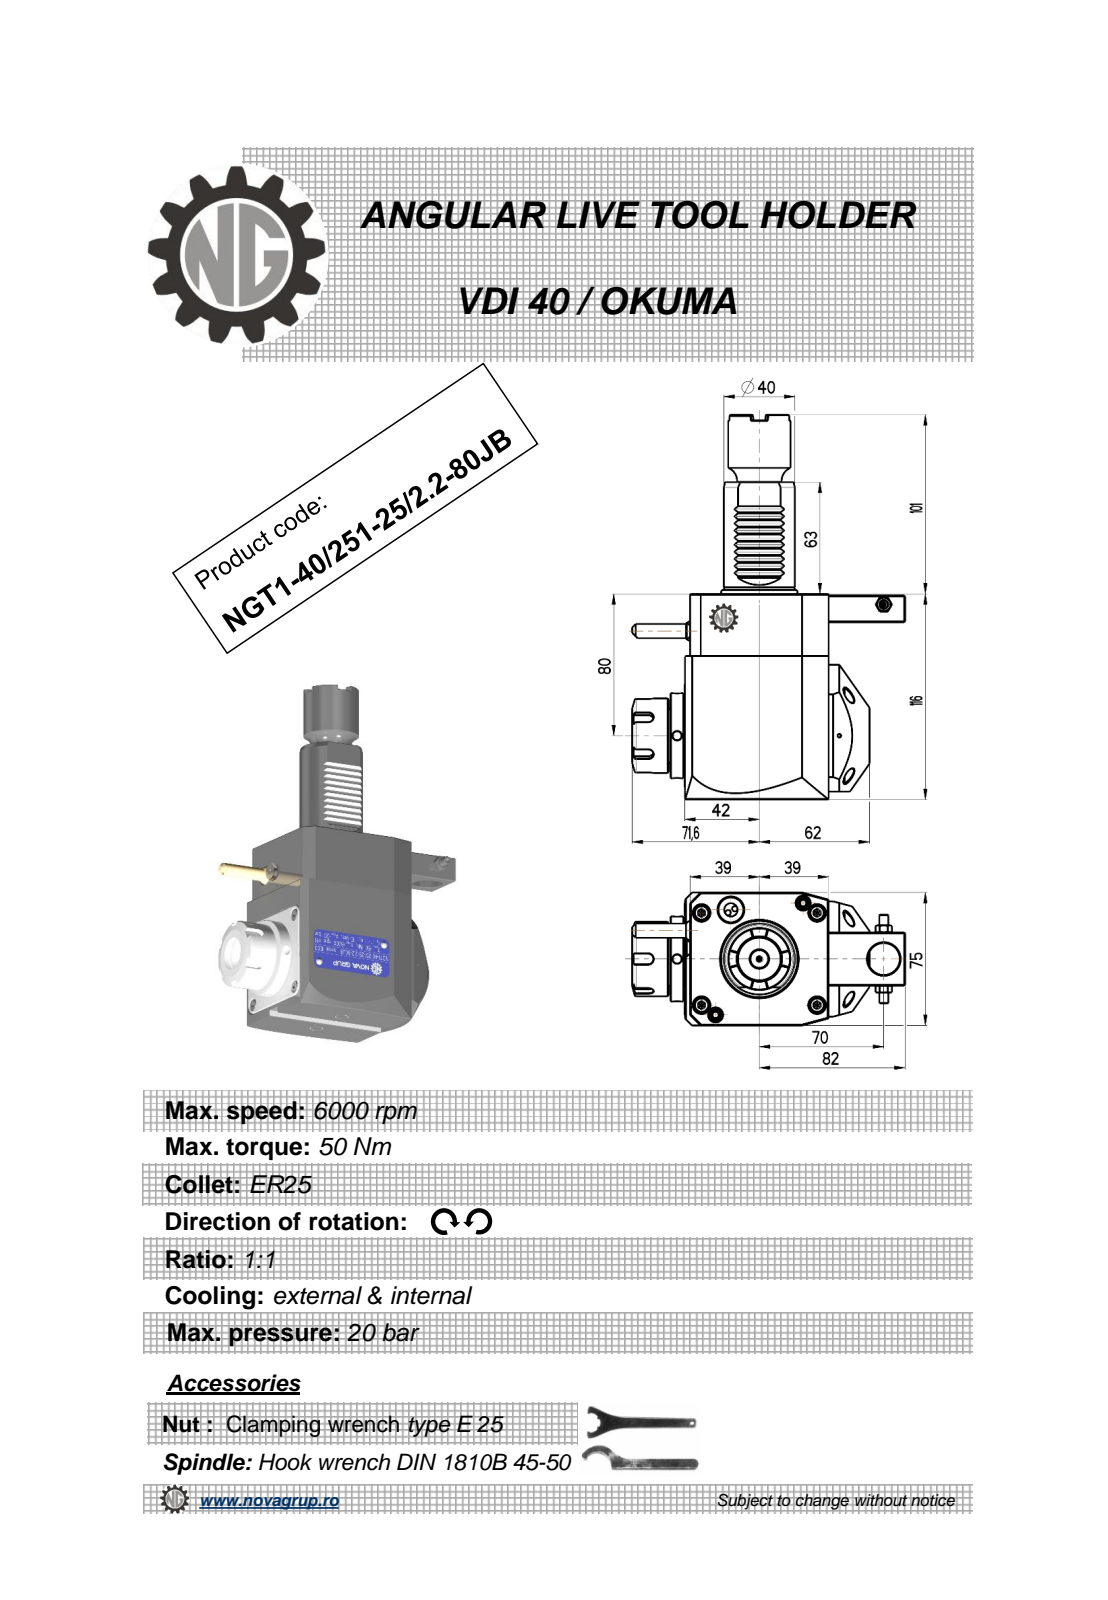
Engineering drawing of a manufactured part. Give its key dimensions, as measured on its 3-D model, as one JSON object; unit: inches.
{"part_name": "NGT1_40_251_25_2_2_80JB", "step_written_by": "PRO/ENGINEER BY PARAMETRIC TECHNOLOGY CORPORATION, 2010280 (CONFIG_CONTROL_DESIGN)", "units": "inches", "bodies": {"solids": 1, "faces": 489, "planar": 210, "cylindrical": 92, "other": 187}, "overall_size": [8.543, 6.047, 3.016], "volume_in3": 55.56, "surface_area_in2": 118.3, "round_holes": [[0.197, 3], [0.118, 1], [0.165, 1], [0.374, 1], [0.709, 1], [0.799, 1], [0.984, 1]], "round_bosses_or_shafts": [[1.89, 1], [1.654, 1], [1.575, 1], [1.476, 1], [1.378, 1], [1.299, 1], [0.394, 1], [0.353, 1]], "partial_cylinders_radius": [[0.01, 12], [0.012, 10], [0.008, 6], [0.118, 5], [0.02, 1], [1.575, 1]], "face_to_face_distances": [2.953, 4.567, 3.189, 0.118, 3.071, 4.409, 0.11, 3.181, 0.039, 3.78], "hole_center_spacings": [0.824, 1.821, 2.407, 2.756, 2.854, 4.577, 5.425]}
